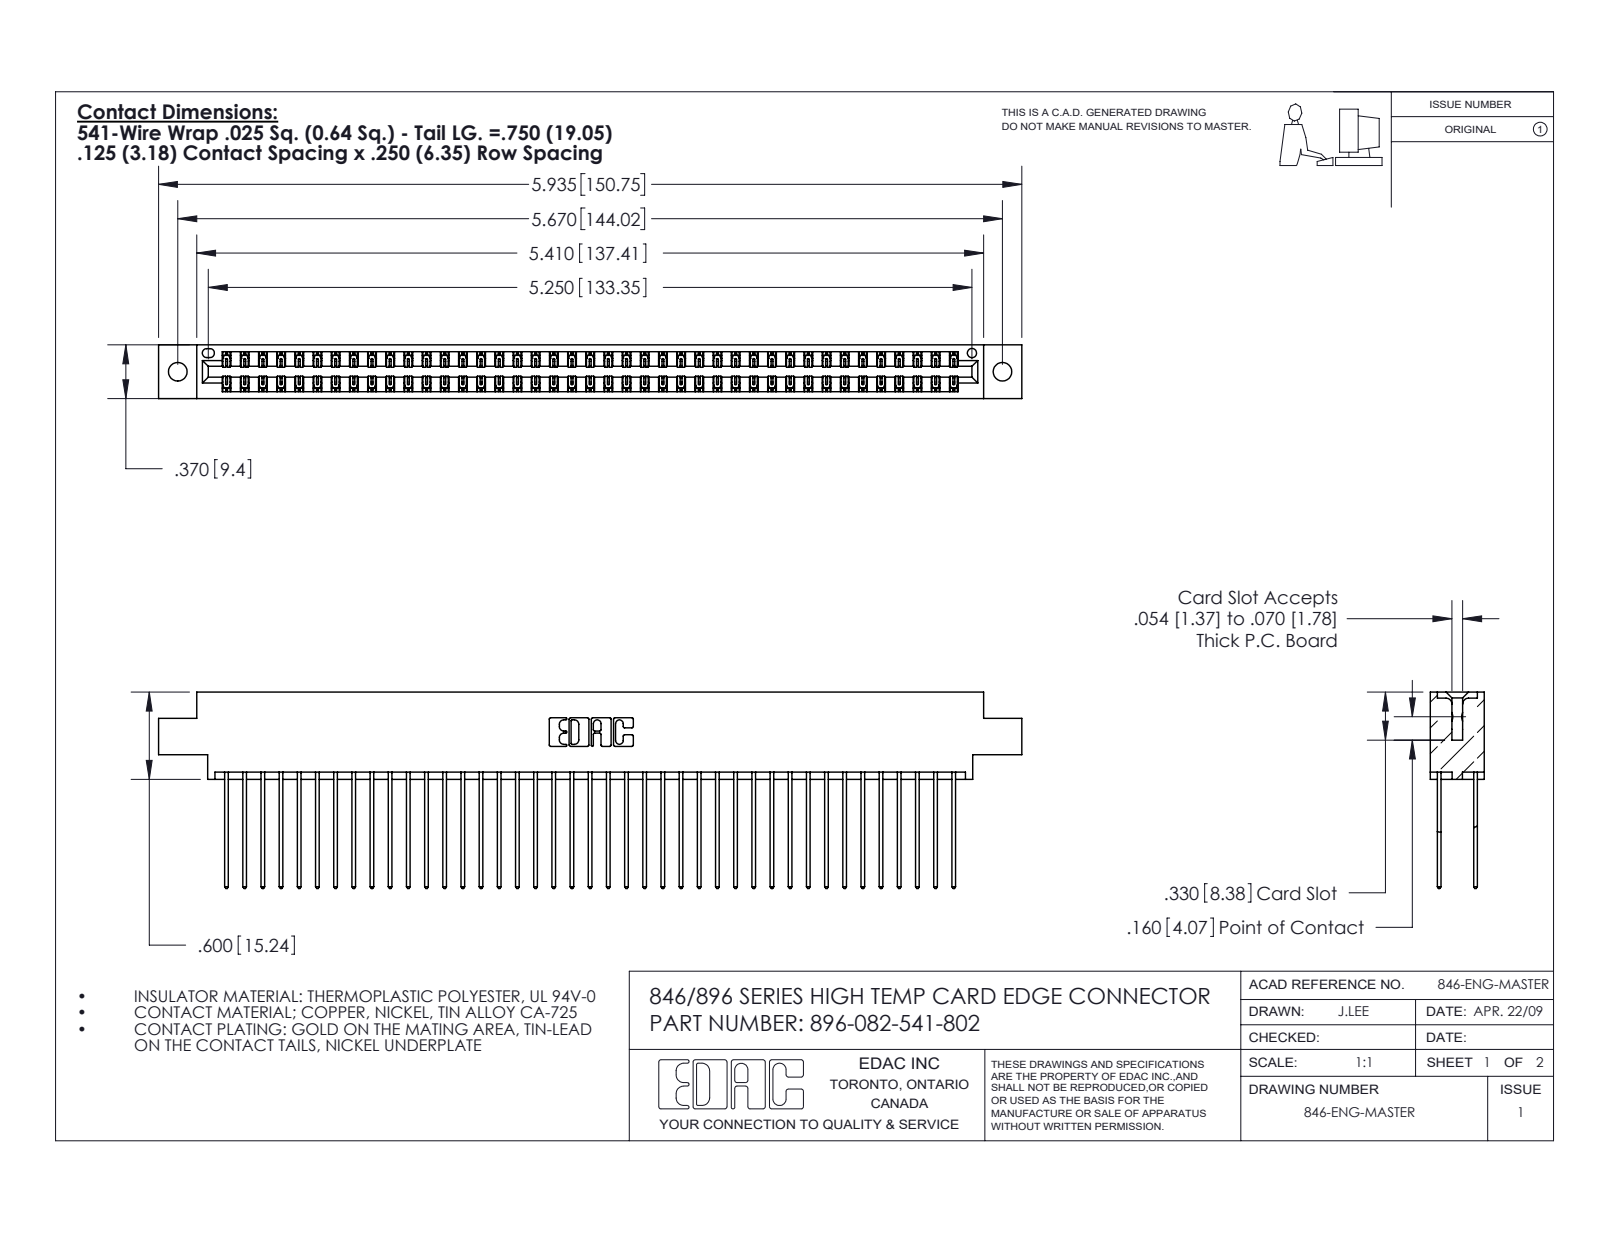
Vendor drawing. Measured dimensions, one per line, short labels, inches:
name: 346 Part_0.170 Offset - 0.128 Dia; 396-082-541-802; 345-292-001_345-293-141
written by: SolidWorks 2016 (CONFIG_CONTROL_DESIGN)
unit: in
bodies: 83 solids, 4390 faces (2950 planar, 1440 cylindrical, 0 other)
size: 5.935 × 1.35 × 0.37
volume: 0.914 in³; area: 35.23 in²
holes: 2× ⌀0.128, 1× ⌀0.064
rounds: 123× R0.006, 82× R0.01, 22× R0.01, 6× R0.007, 6× R0.031, 3× R0.026, 2× R0.014, 2× R0.022
face distances: 0.048, 0.322, 0.25, 0.072, 0.298, 0.025, 0.37, 0.275, 0.225, 0.148
hole spacings: 0.246, 5.461, 5.67
